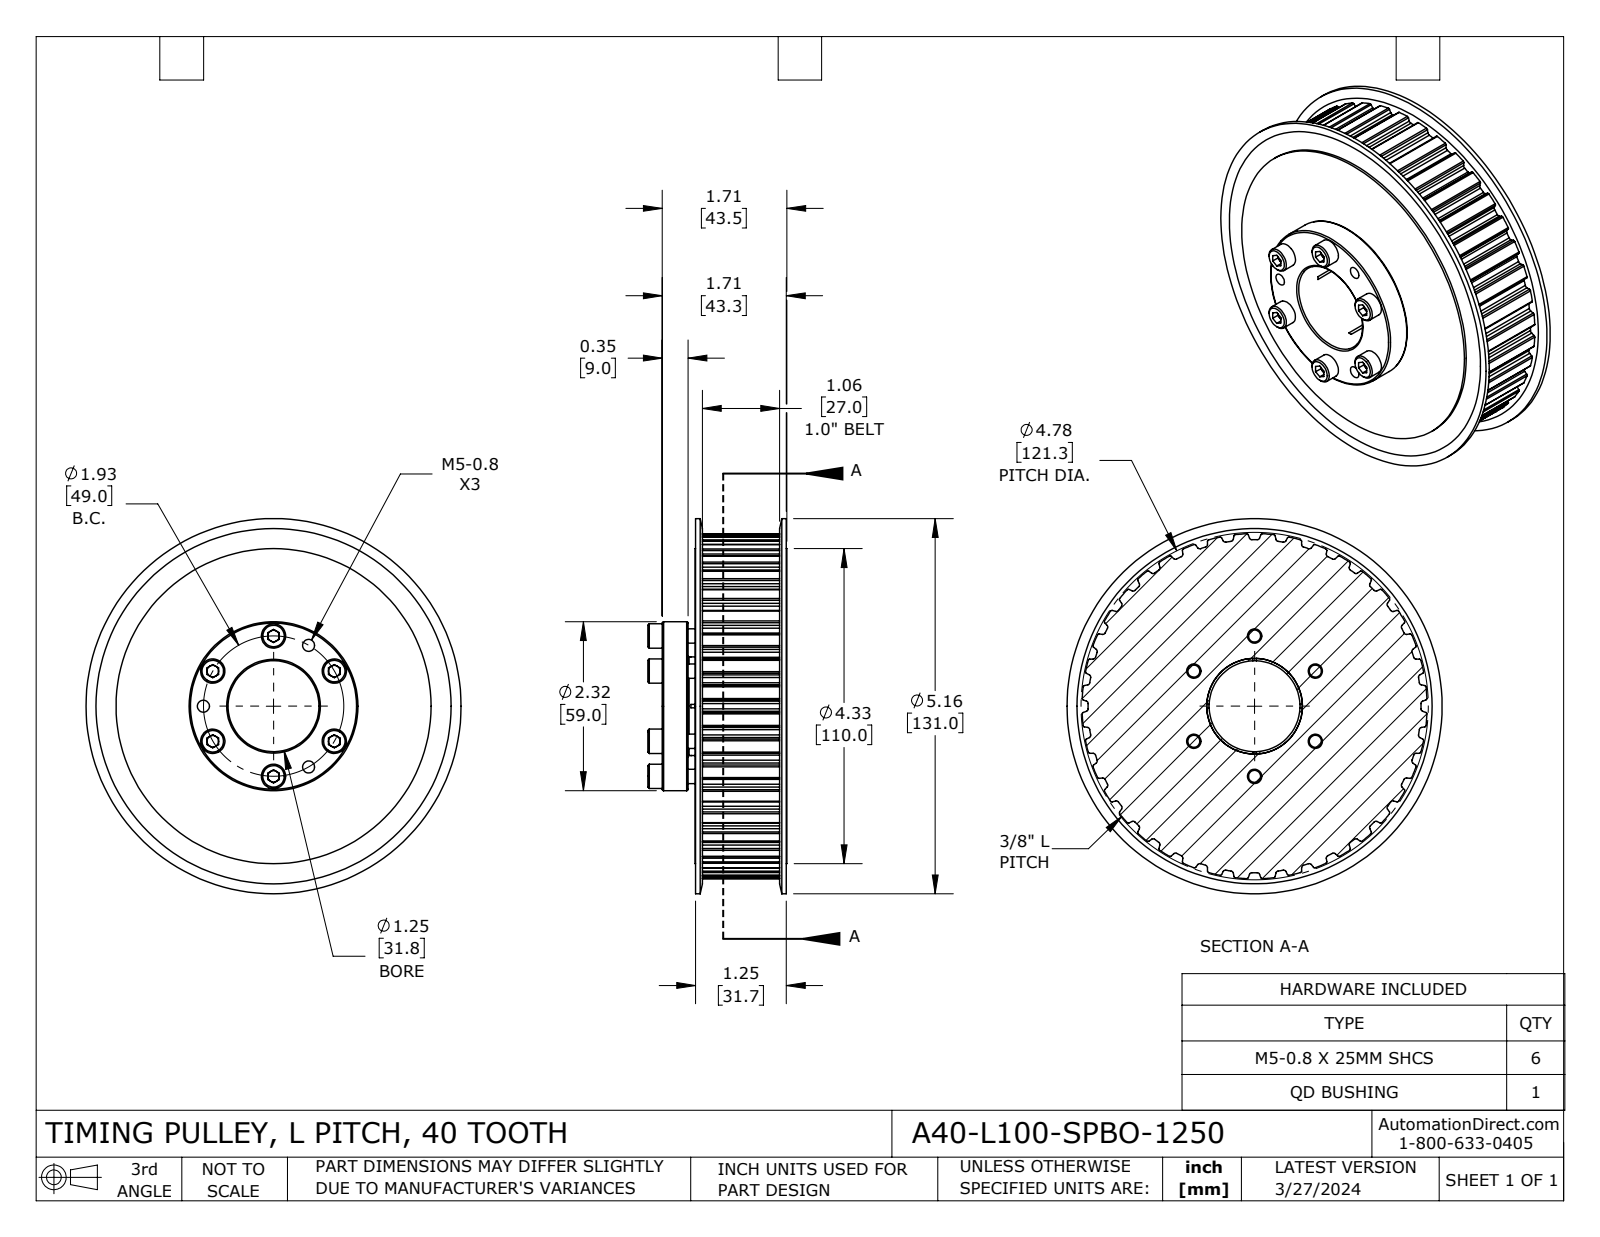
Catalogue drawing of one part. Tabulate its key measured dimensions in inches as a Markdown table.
| quantity | value |
| --- | --- |
| part name | A40-L100-SPBO-1250 |
| STEP written by | SolidWorks 2021 (CONFIG_CONTROL_DESIGN) |
| units | inches |
| bodies | 10 solids, 619 faces (196 planar, 349 cylindrical, 74 other) |
| overall size | 5.157 × 5.157 × 1.909 |
| volume | 21.51 in³ |
| surface area | 113.1 in² |
| round holes (diameter × count) | 0.165 × 9, 0.217 × 6, 1.25 × 1, 1.358 × 1, 4.331 × 1 |
| round bosses / shafts (diameter × count) | 0.335 × 6, 0.197 × 6, 5.157 × 1, 2.323 × 1 |
| partial cylindrical surfaces (radius × count) | 0.021 × 80, 0.034 × 80, 2.288 × 1, 2.372 × 1 |
| main face-to-face distances | 1.26, 0.098, 1.161, 0.035, 1.224, 0.063, 1.126, 1.063, 1.189, 0.551 |
| hole center spacings | 0.965, 1.671, 1.364, 1.863, 0.499, 1.929, 0.5 |
